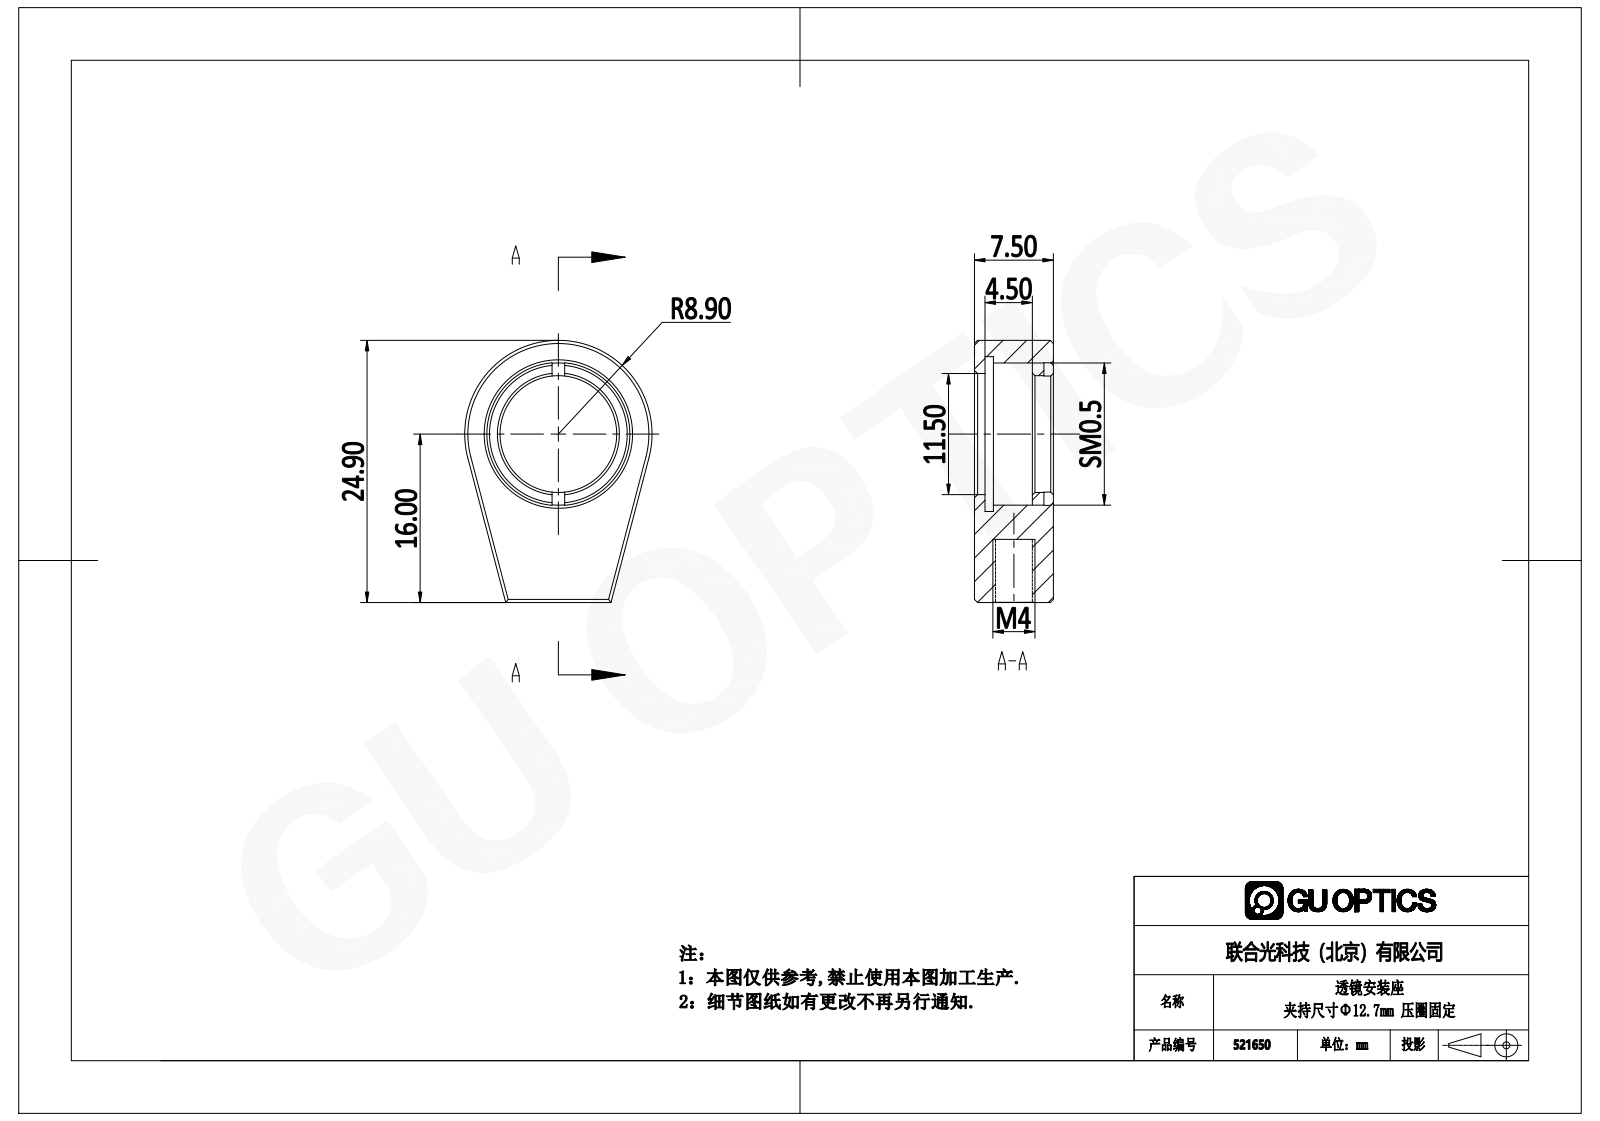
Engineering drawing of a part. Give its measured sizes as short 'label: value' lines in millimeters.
name: 1.3.1.1-ZZT-0.5
written by: SolidWorks 2021 (CONFIG_CONTROL_DESIGN)
unit: mm
bodies: 0 solids, 55 faces (22 planar, 13 cylindrical, 20 other)
size: 24.9 × 17.8 × 7.5
holes: 1× ⌀4, 1× ⌀11.09, 1× ⌀11.5, 1× ⌀13.5, 1× ⌀14.7
rounds: 1× R8.9
face distances: 7.5, 1, 6.5, 5.5, 4.5, 2, 1.8, 0.8, 3.7, 5.7
